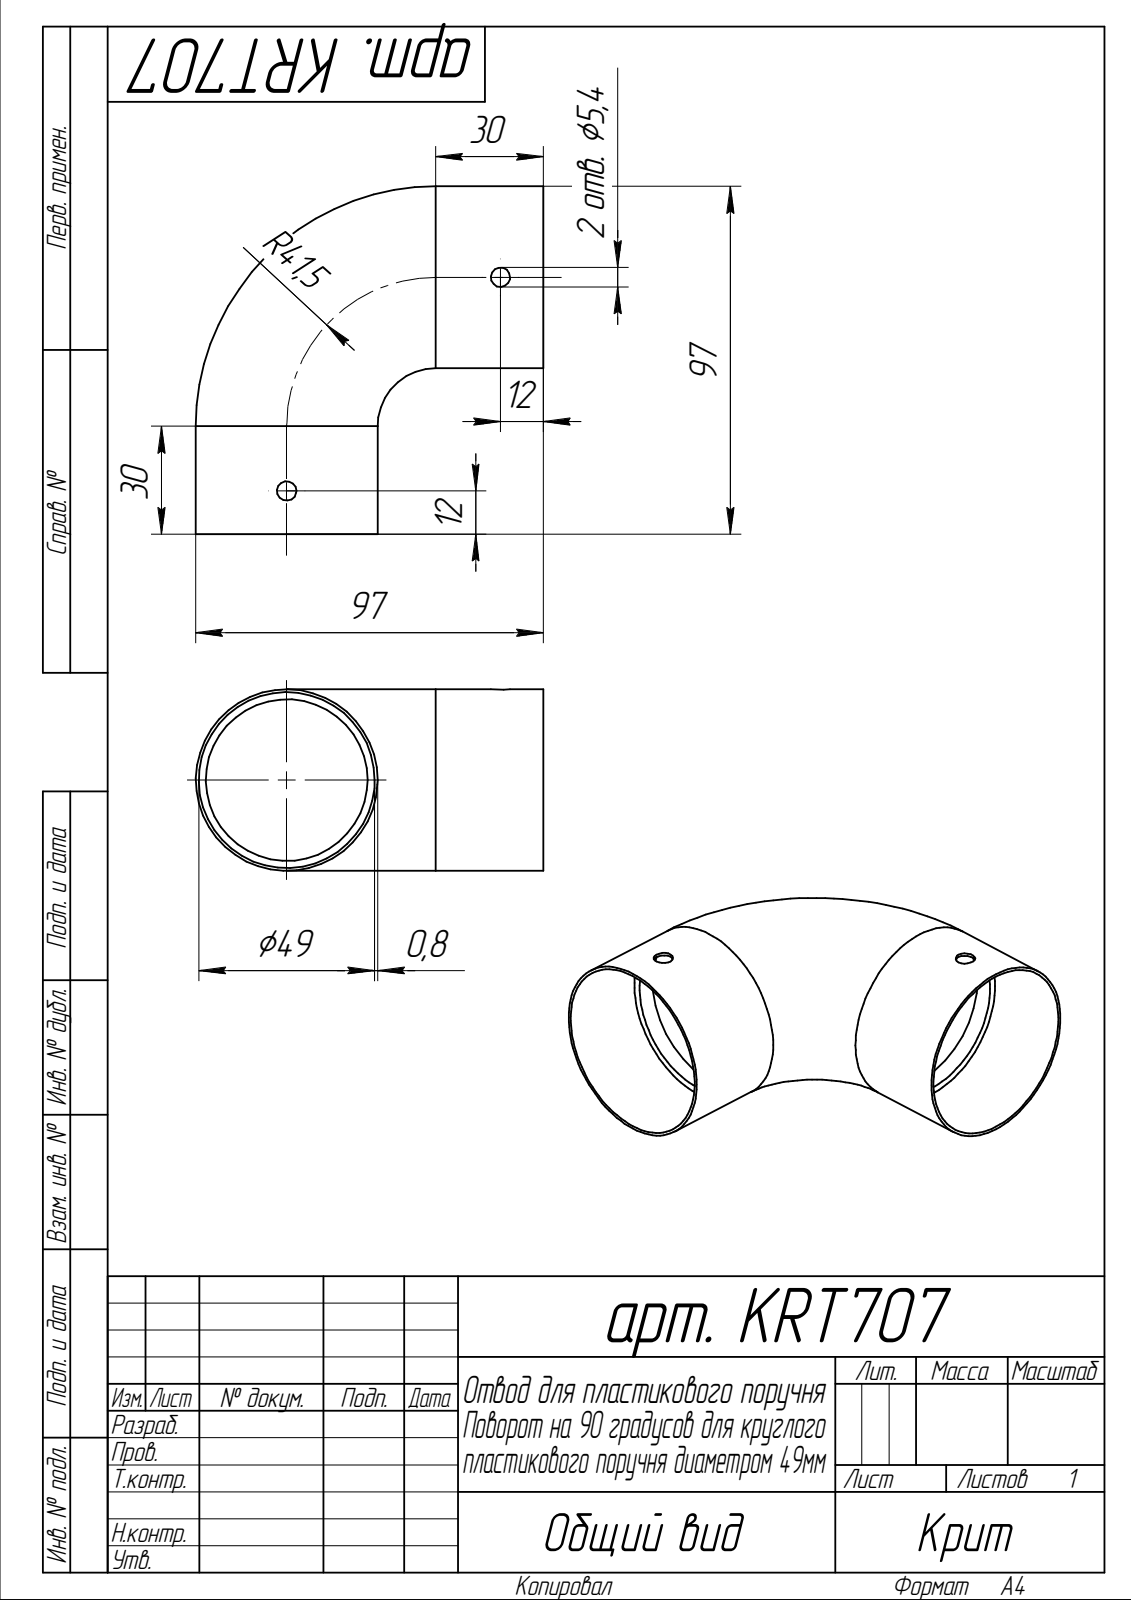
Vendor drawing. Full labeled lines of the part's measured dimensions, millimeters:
Part name (STEP PRODUCT): арт. KRT707
STEP written by: SolidWorks 2014 (AUTOMOTIVE_DESIGN)
Units: millimetres
Bodies: 1 solid, 26 faces (6 planar, 16 cylindrical, 4 other)
Overall size (bounding box): 96.8 × 96.8 × 50.6
Volume: 18 585 mm³ · Surface area: 40 413 mm²
Round holes (diameter × count): ⌀5.4 ×2, ⌀45 ×2, ⌀49 ×2
Round bosses / shafts (diameter × count): ⌀50.6 ×2
Main face-to-face distances: 5, 30, 25
Hole centre spacings: 84.15
